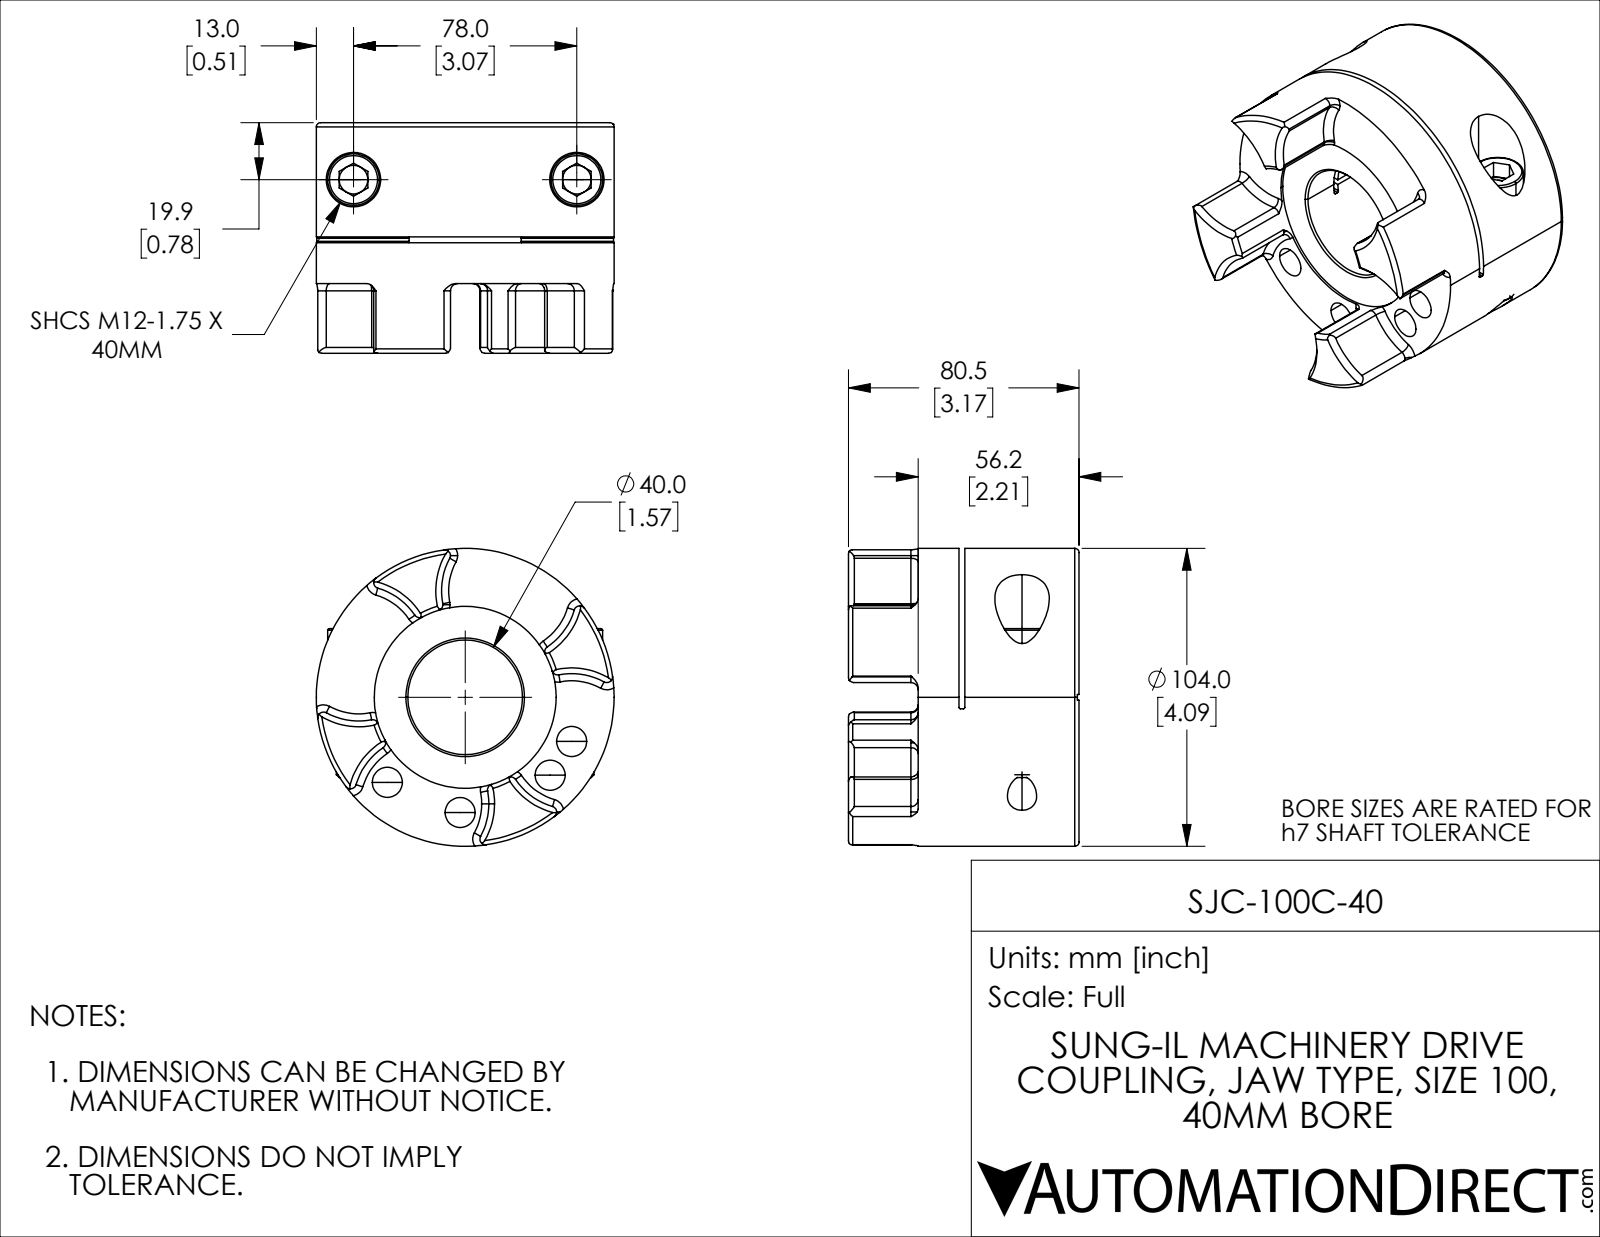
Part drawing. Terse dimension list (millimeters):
name: SJC-100C-40
written by: SolidWorks 2021 (CONFIG_CONTROL_DESIGN)
unit: mm
bodies: 3 solids, 215 faces (52 planar, 78 cylindrical, 85 other)
size: 104 × 104 × 80.5
volume: 414 832 mm³; area: 70 797 mm²
holes: 4× ⌀10.5, 2× ⌀10, 2× ⌀10.2, 2× ⌀12.5, 2× ⌀19, 1× ⌀40, 1× ⌀63.5
bosses: 2× ⌀18, 2× ⌀12, 1× ⌀104
rounds: 16× R2, 4× R23.68, 2× R0.5, 1× R75
face distances: 2, 41.9, 39.9, 56.2, 16.3, 14.3, 55.3, 15.4, 13.4, 0.9
hole spacings: 40.25, 13.98, 27.52, 34.03, 46.18, 56.92, 65.94, 78
